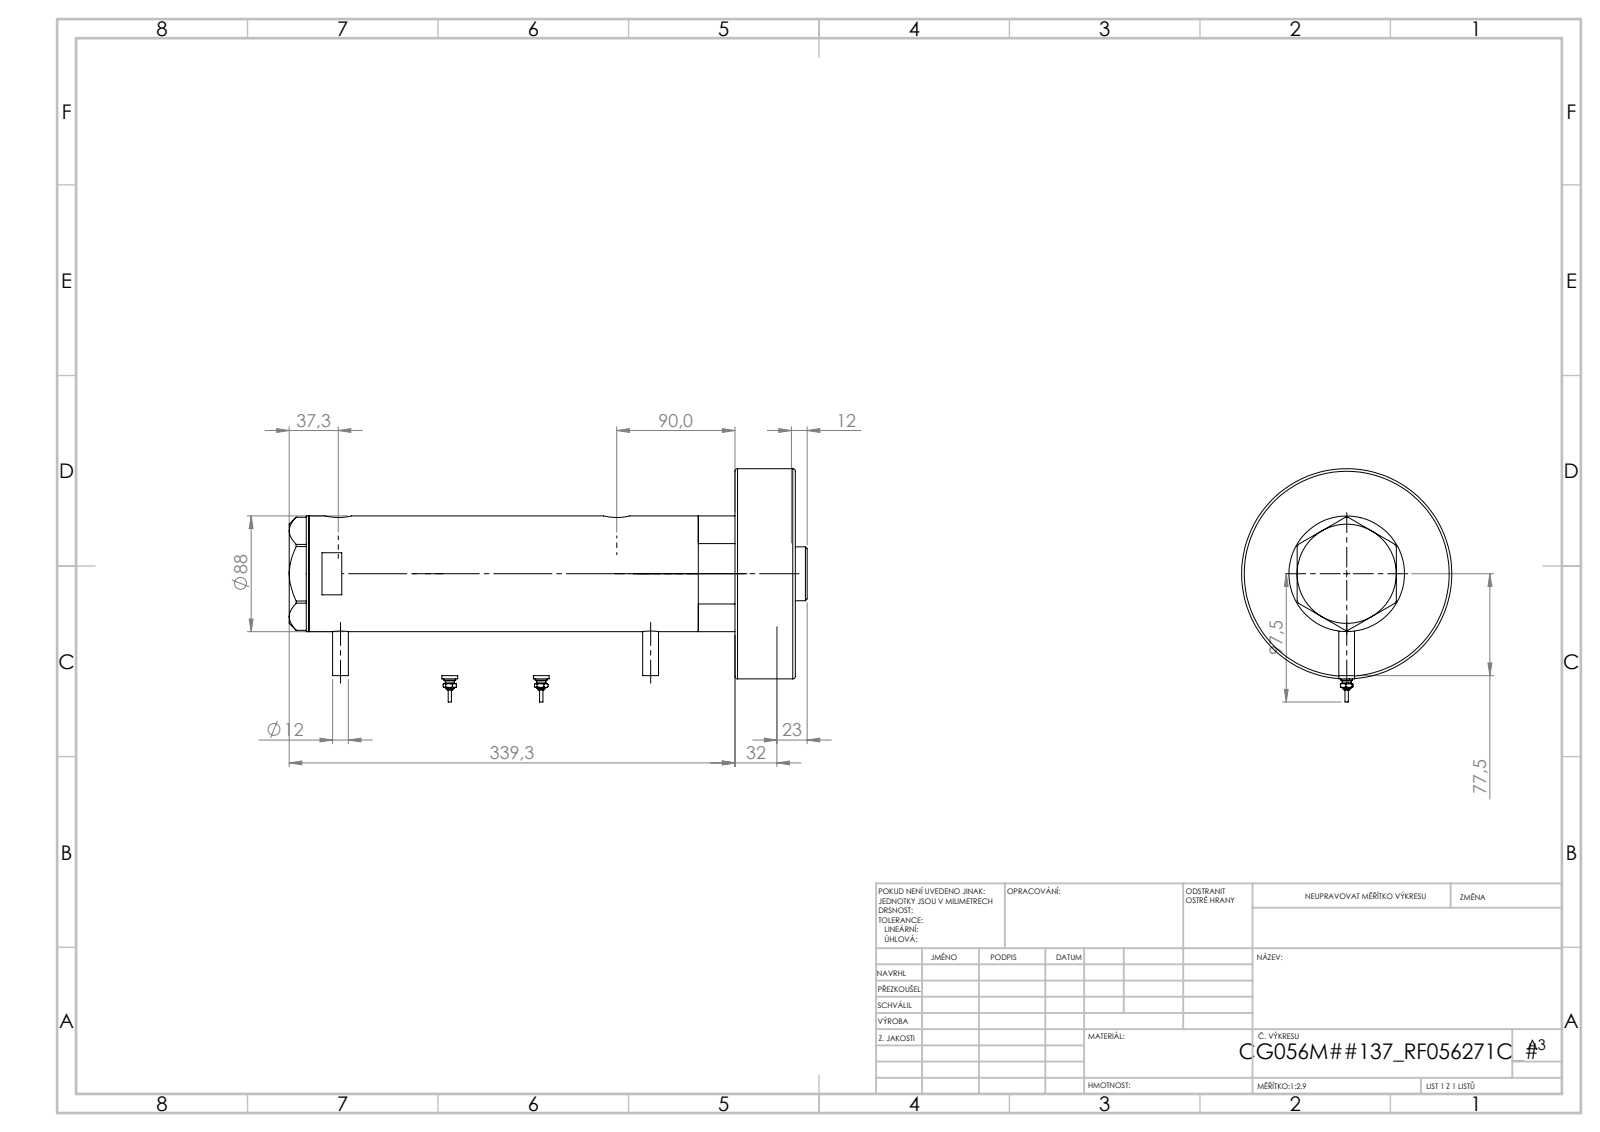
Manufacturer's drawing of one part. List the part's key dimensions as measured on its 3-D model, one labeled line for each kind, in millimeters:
Part name (STEP PRODUCT): V270CG_MIDDLE; V270CG_271C; V270CG_VC; V270CG_BACK (+2 more)
STEP written by: SolidWorks 2019 (CONFIG_CONTROL_DESIGN)
Units: millimetres
Bodies: 7 solids, 242 faces (83 planar, 81 cylindrical, 78 other)
Overall size (bounding box): 361.47 × 160 × 160
Volume: 2 571 000 mm³ · Surface area: 326 731 mm²
Round holes (diameter × count): ⌀5 ×2, ⌀12.5 ×2, ⌀13.16 ×2, ⌀20 ×2, ⌀14.5 ×1, ⌀42 ×1, ⌀43.5 ×1, ⌀56 ×1, ⌀60 ×1, ⌀75 ×1, ⌀80 ×1
Round bosses / shafts (diameter × count): ⌀12 ×2, ⌀9 ×2, ⌀7 ×2, ⌀4.34 ×2, ⌀2.4 ×2, ⌀160 ×1, ⌀88 ×1, ⌀73 ×1
Main face-to-face distances: 46, 288.9, 334.9, 211.4, 77.5, 123.5, 26, 185.4, 262.9, 308.9
Hole centre spacings: 1.7, 25.8, 187.3, 189, 213.1, 214.8
